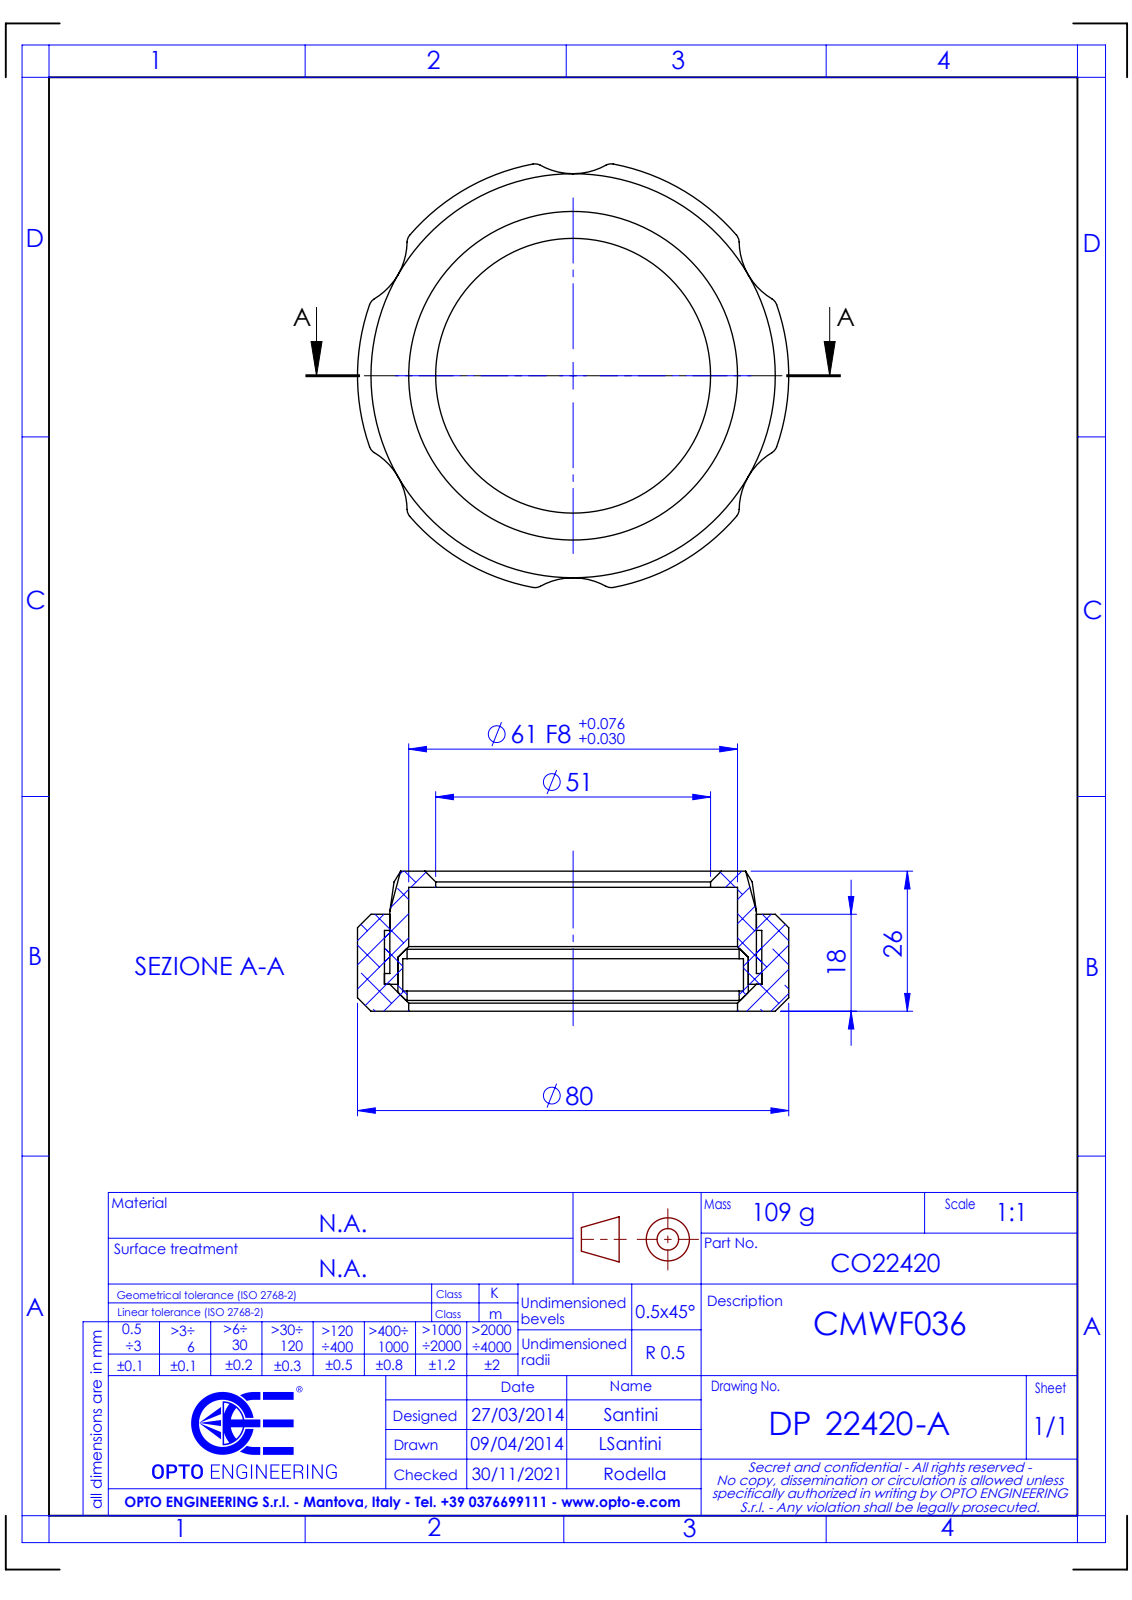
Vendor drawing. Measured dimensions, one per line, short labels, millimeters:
name: DP22420 -A_CMWF036
written by: SolidWorks 2021 (CONFIG_CONTROL_DESIGN)
unit: mm
bodies: 0 solids, 93 faces (11 planar, 56 cylindrical, 26 other)
size: 80 × 78.67 × 26
holes: 1× ⌀51, 1× ⌀61, 1× ⌀61.6, 1× ⌀63.2, 1× ⌀65
bosses: 1× ⌀68
rounds: 12× R2, 7× R40, 6× R12.5
face distances: 5, 18, 3, 23, 26, 8, 21, 13, 9.75, 4.75
